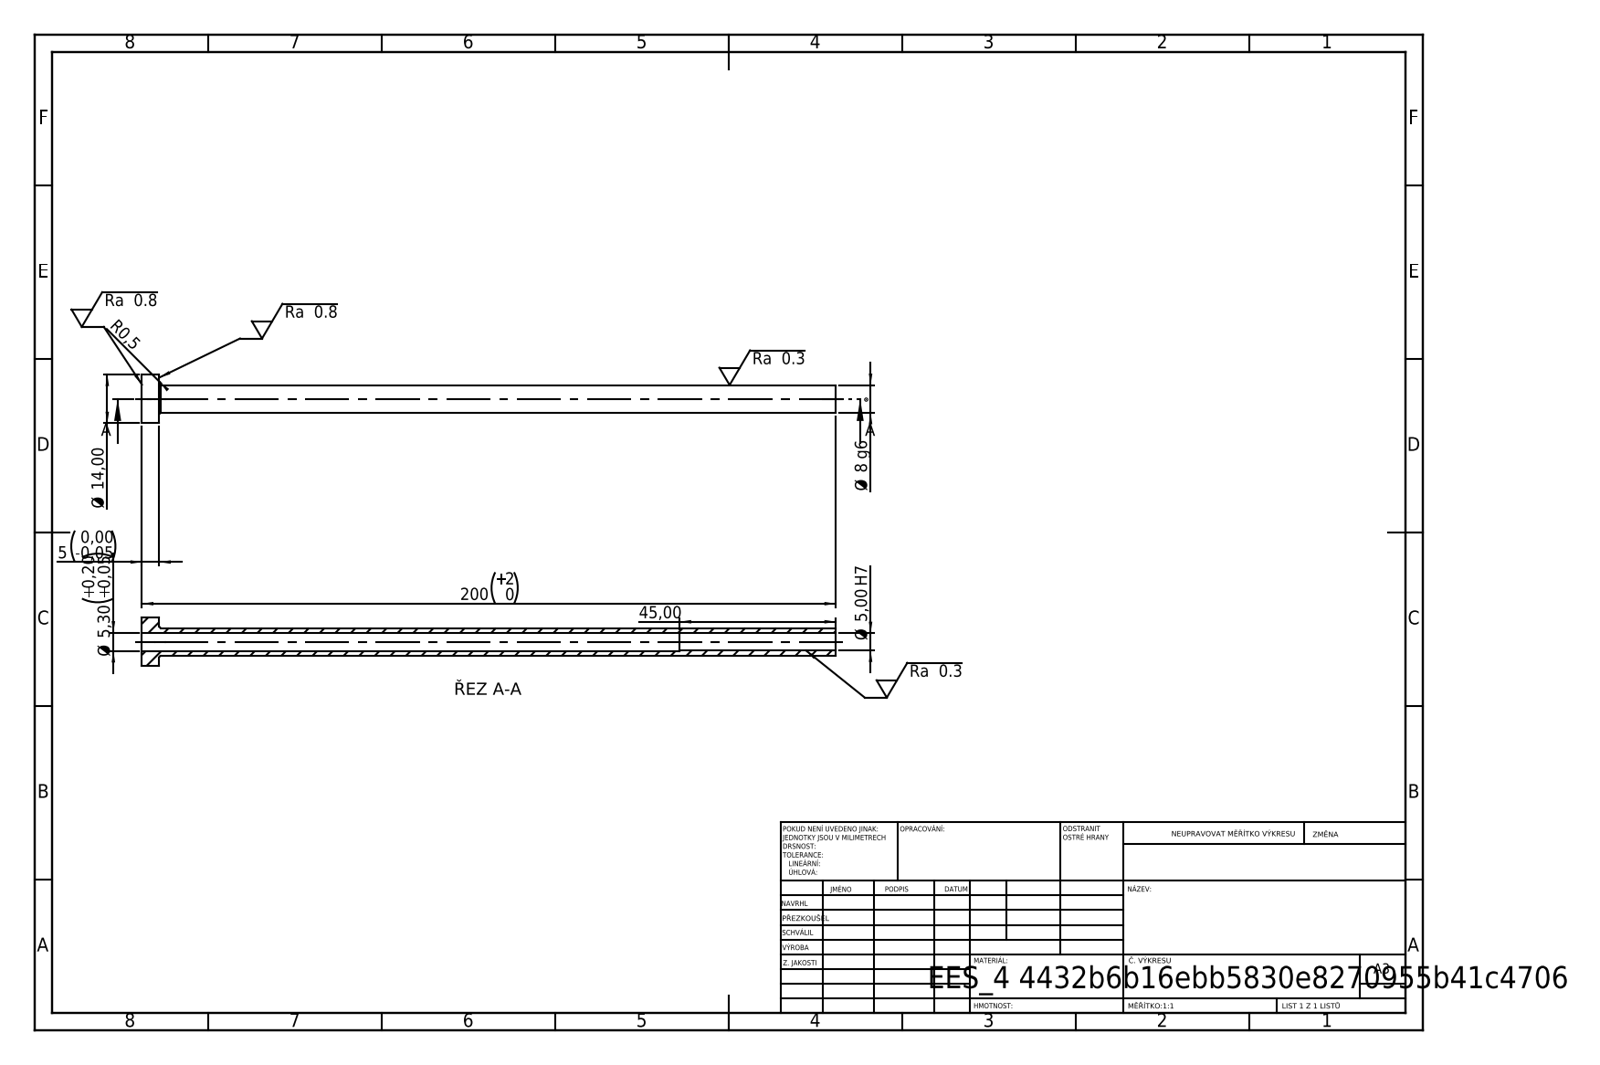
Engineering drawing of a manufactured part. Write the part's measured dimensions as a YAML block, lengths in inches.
step_written_by: "SolidWorks 2019 (CONFIG_CONTROL_DESIGN)"
units: inches
bodies: {solids: 1, faces: 14, planar: 4, cylindrical: 8, other: 2}
overall_size: [7.874, 0.551, 0.551]
volume: 0.383
surface_area: 13.44
round_holes:
  - {diameter: 0.197, count: 1}
  - {diameter: 0.209, count: 1}
round_bosses_or_shafts:
  - {diameter: 0.551, count: 1}
  - {diameter: 0.315, count: 1}
face_to_face_distances: [0.197, 7.874, 7.677, 6.102, 5.906, 1.772]
